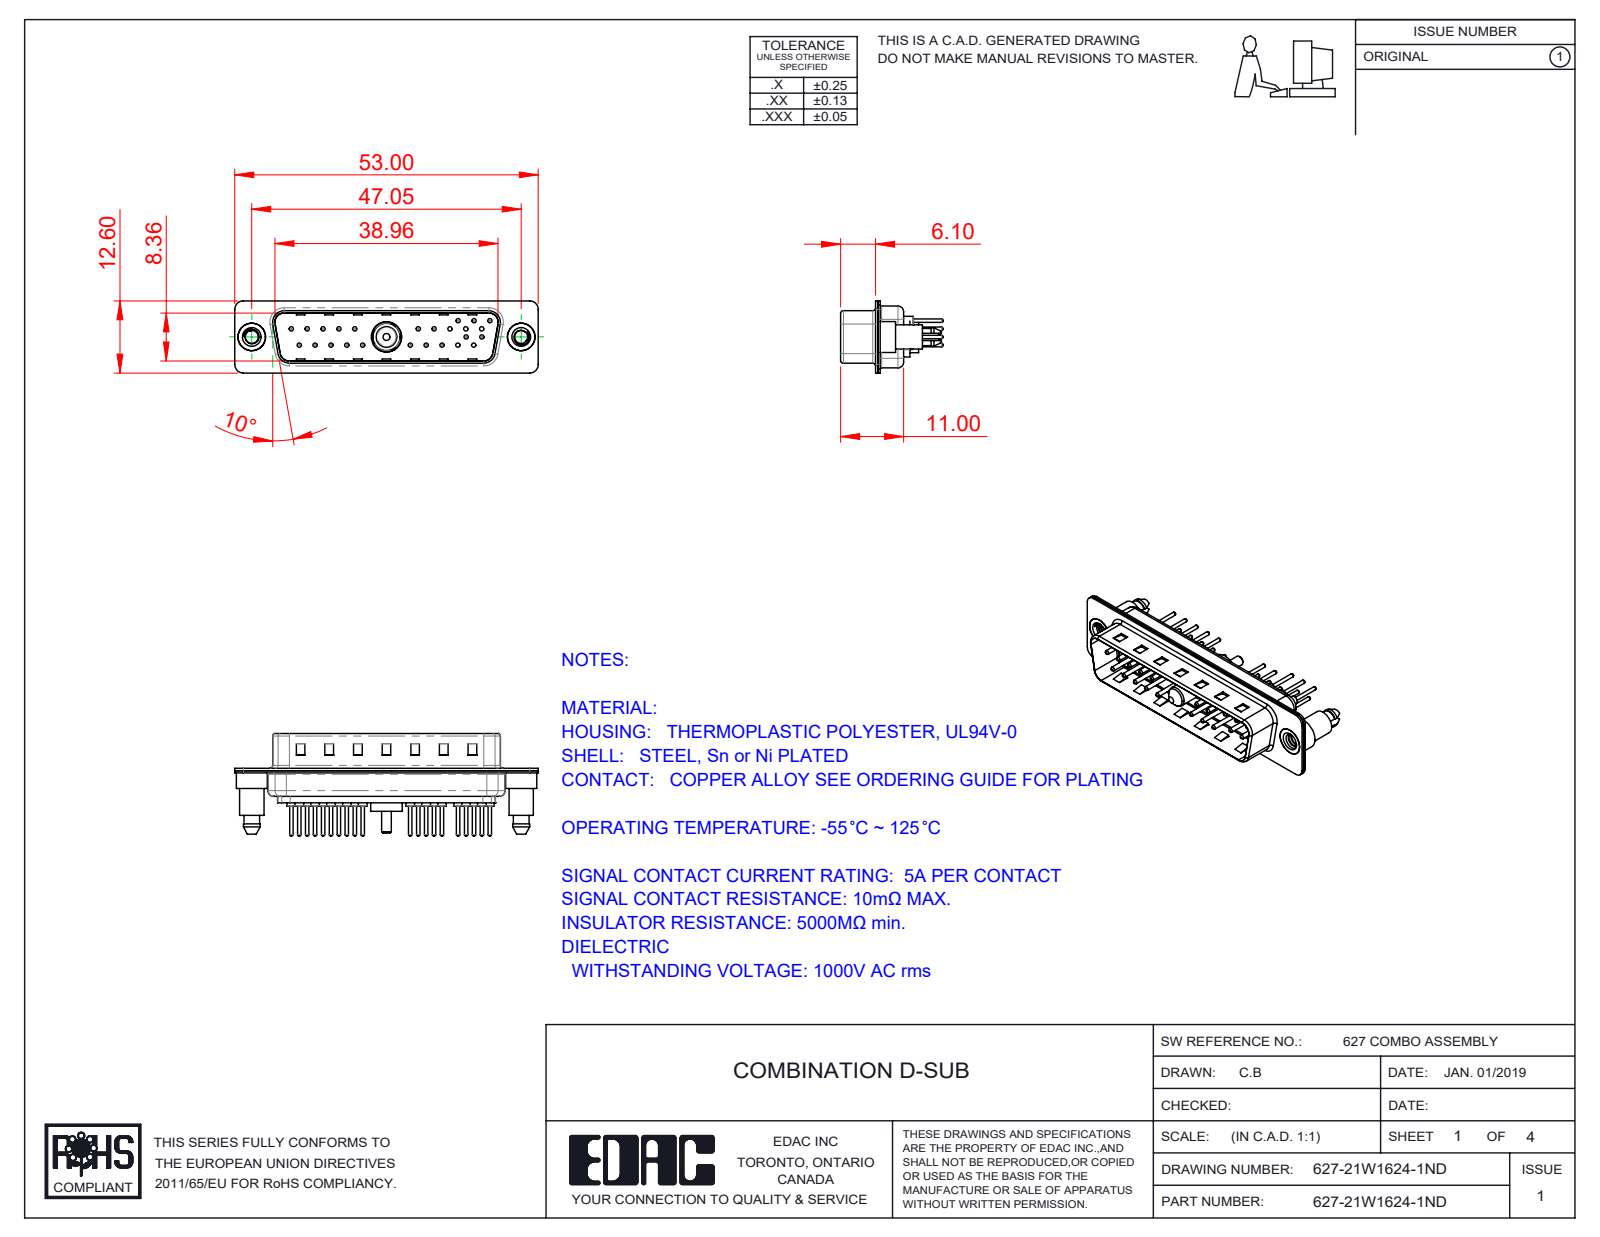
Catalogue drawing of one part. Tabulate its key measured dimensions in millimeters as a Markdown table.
| quantity | value |
| --- | --- |
| part name | 627Combo Threaded Boardlock_D; 627Combo Shell Front_25 Contacts; 627Combo Shell Rear_25 Contacts; 627-21W1624-1ND (+5 more) |
| STEP written by | SolidWorks 2016 (CONFIG_CONTROL_DESIGN) |
| units | millimeters |
| bodies | 27 solids, 1214 faces (337 planar, 476 cylindrical, 401 other) |
| overall size | 53 × 17.9 × 12.6 |
| volume | 2 907 mm³ |
| surface area | 7 151 mm² |
| round holes (diameter × count) | 0.75 × 20, 1.6 × 20, 2 × 20, 2.26 × 2, 4 × 2, 4.8 × 2, 4.85 × 1, 5.3 × 1 |
| round bosses / shafts (diameter × count) | 1.5 × 20, 0.6 × 20, 2 × 5, 0.75 × 5, 5.4 × 2, 4.9 × 2, 4.25 × 2, 5.5 × 1 |
| partial cylindrical surfaces (radius × count) | 1.5 × 18, 2 × 12, 1.6 × 10, 0.5 × 8, 0.25 × 4, 0.6 × 4, 0.65 × 4, 0.9 × 4 |
| main face-to-face distances | 0.4, 0.82, 9.58, 8.76, 1.5, 5.2, 5.6, 0.8, 6, 1.22 |
| hole center spacings | 3.16, 2.77, 5.54, 8.31, 5.04, 19.39, 20.97, 22.16 |
